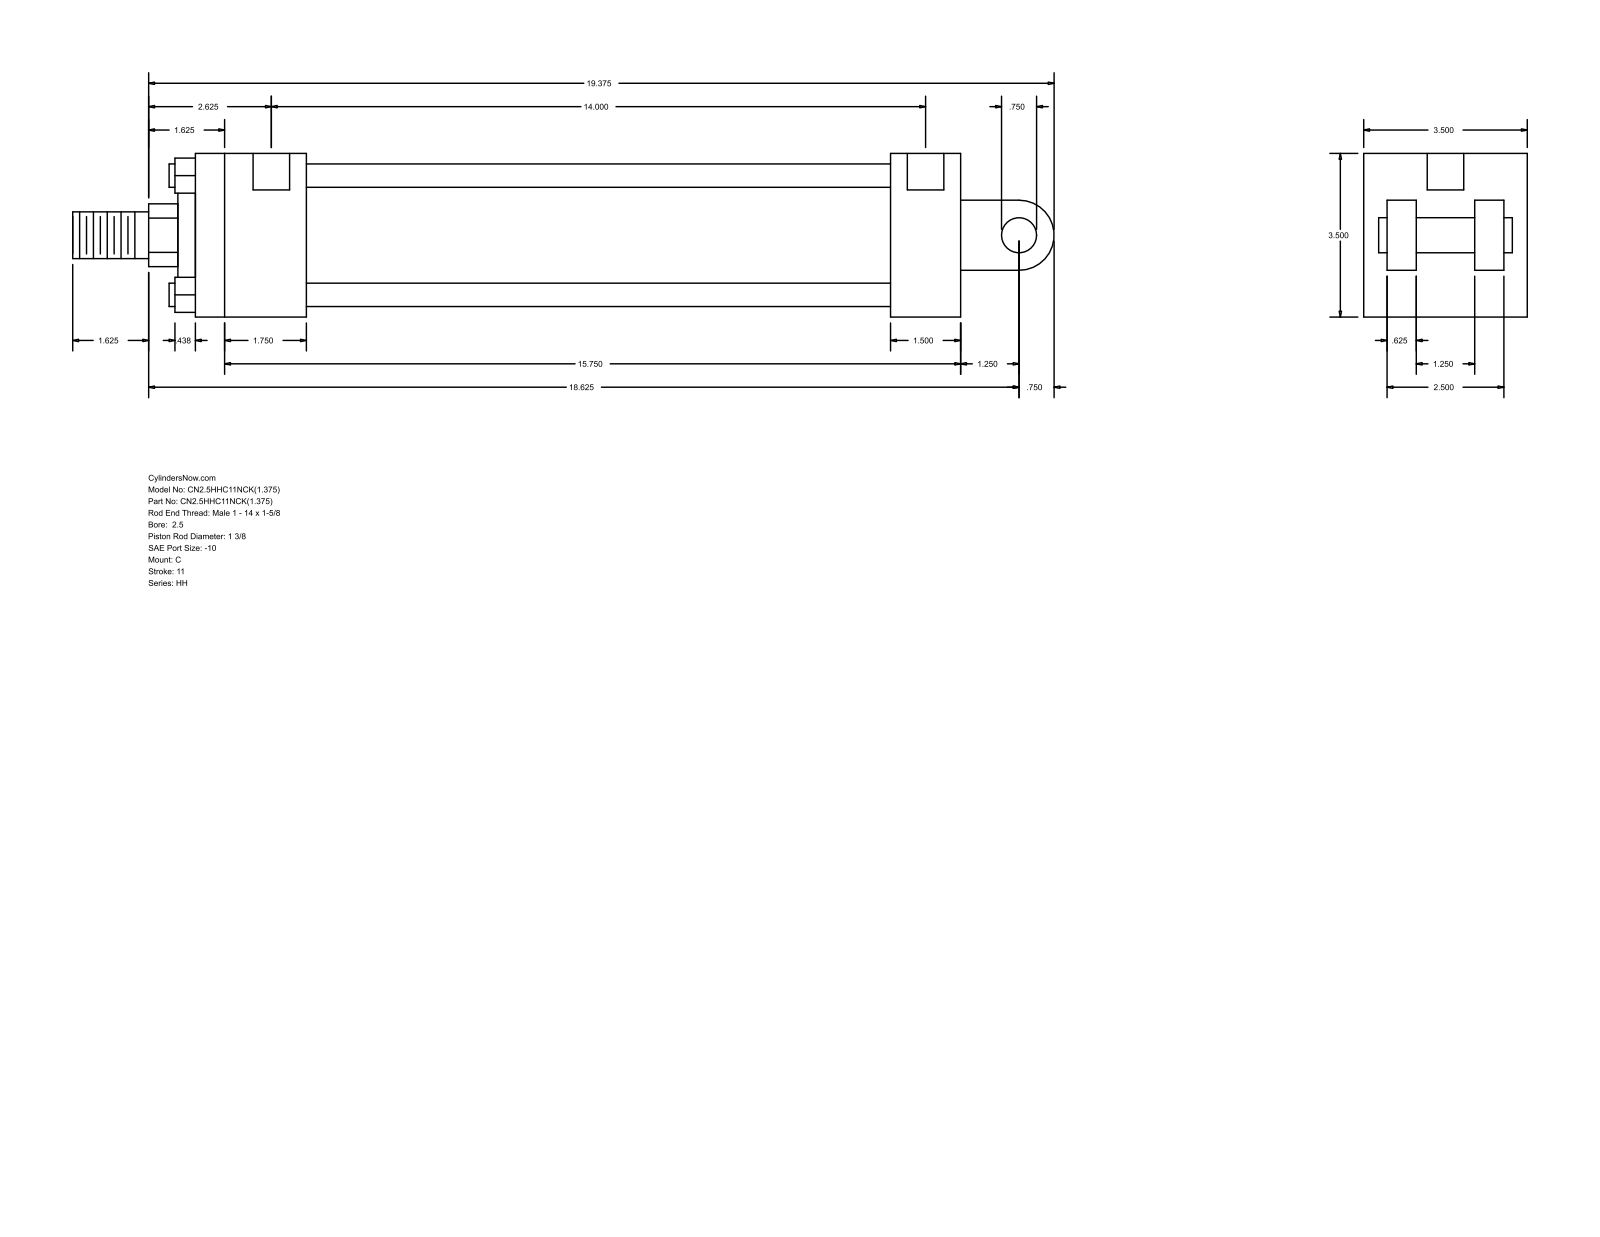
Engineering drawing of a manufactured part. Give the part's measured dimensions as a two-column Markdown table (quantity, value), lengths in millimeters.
| quantity | value |
| --- | --- |
| part name | HH_C__0250_1.375 |
| STEP written by | GSSL Pune (CONFIG_CONTROL_DESIGN) |
| units | millimeters |
| bodies | 0 solids, 99 faces (70 planar, 29 cylindrical, 0 other) |
| overall size | 533.4 × 88.9 × 88.9 |
| round holes (diameter × count) | 5.56 × 4, 19.84 × 2 |
| round bosses / shafts (diameter × count) | 12.7 × 4, 73.03 × 1, 50.8 × 1, 34.92 × 1, 25.4 × 1, 19.05 × 1 |
| partial cylindrical surfaces (radius × count) | 17.06 × 1, 19.05 × 1 |
| main face-to-face distances | 88.9, 415.92, 63.5, 12.7, 377.83, 38.09, 60.32, 317.51, 355.6, 76.2 |
| hole center spacings | 358.77, 1.58, 1.59, 355.6, 357.18, 357.19 |
